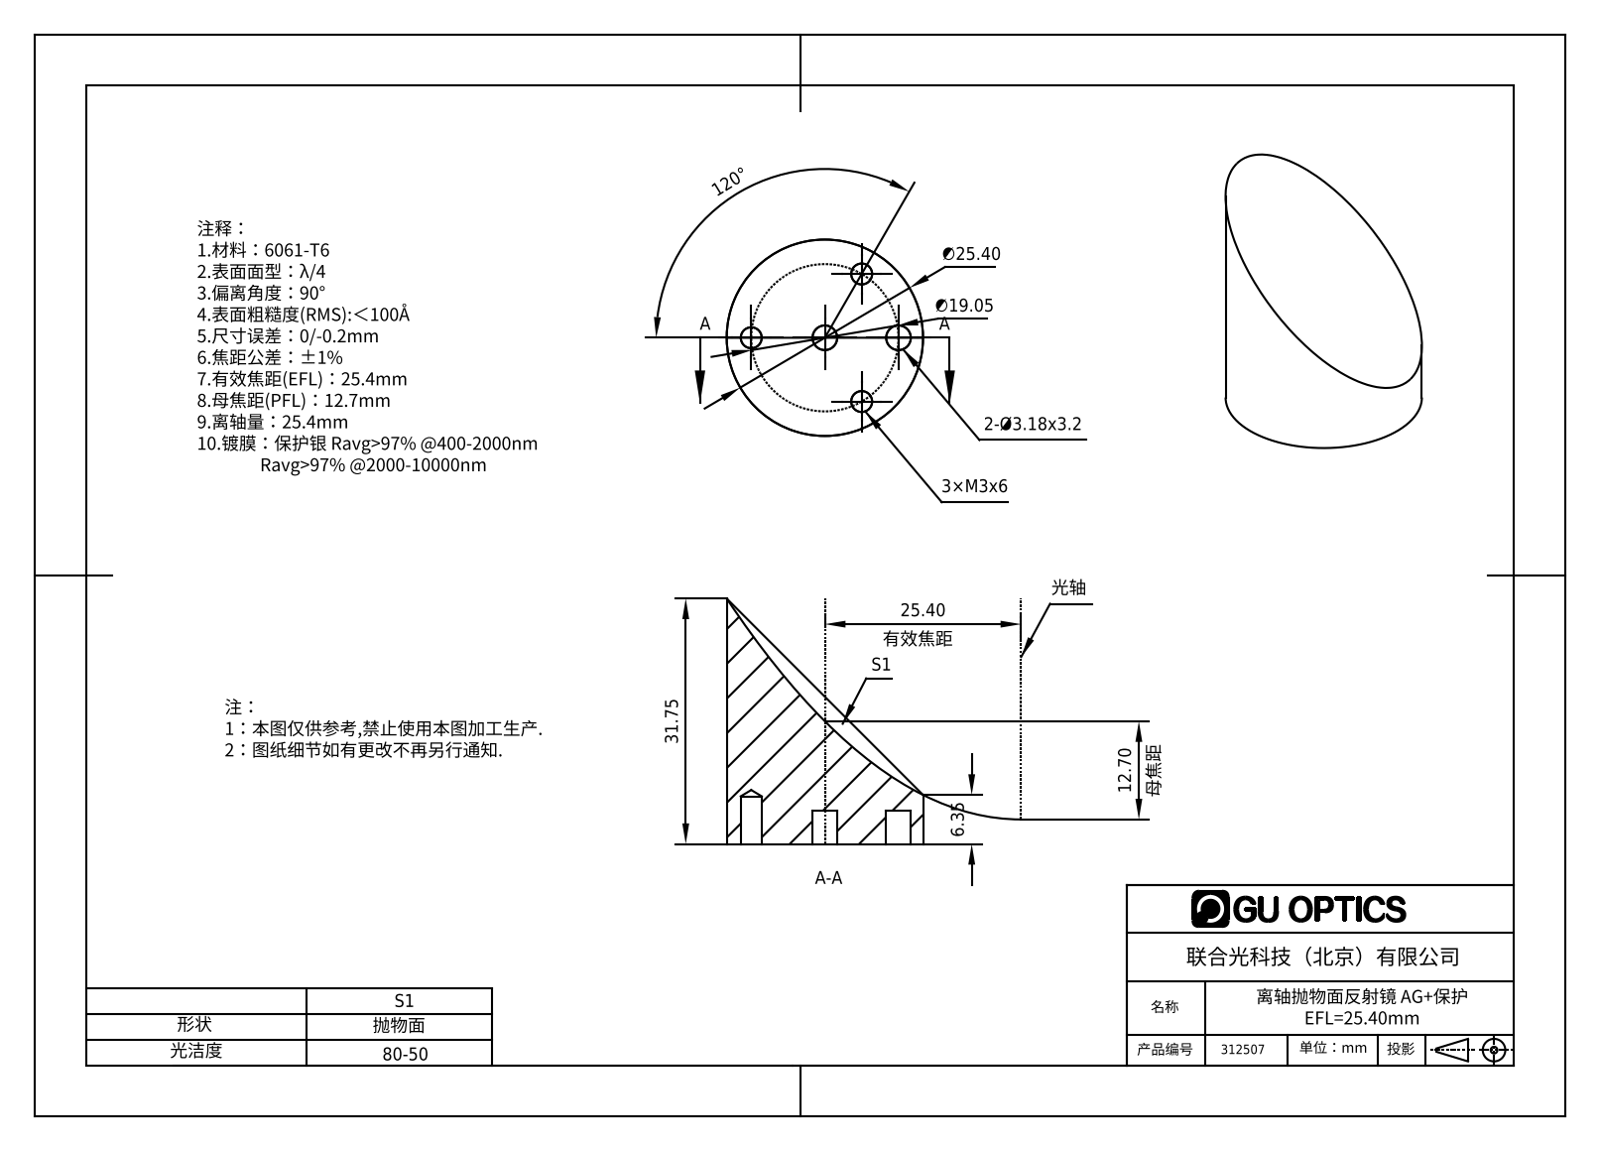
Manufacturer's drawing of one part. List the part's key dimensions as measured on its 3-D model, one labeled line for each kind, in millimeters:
Part name (STEP PRODUCT): Ø25_35500
STEP written by: SolidWorks 2018 (CONFIG_CONTROL_DESIGN)
Units: millimetres
Bodies: 1 solid, 23 faces (3 planar, 12 cylindrical, 8 other)
Overall size (bounding box): 31.75 × 25.4 × 25.4
Volume: 8 668 mm³ · Surface area: 3 007 mm²
Round holes (diameter × count): ⌀2.71 ×3, ⌀3.19 ×2
Round bosses / shafts (diameter × count): ⌀25.4 ×1
Main face-to-face distances: 4.32
Hole centre spacings: 9.53, 16.5, 9.52, 19.06
